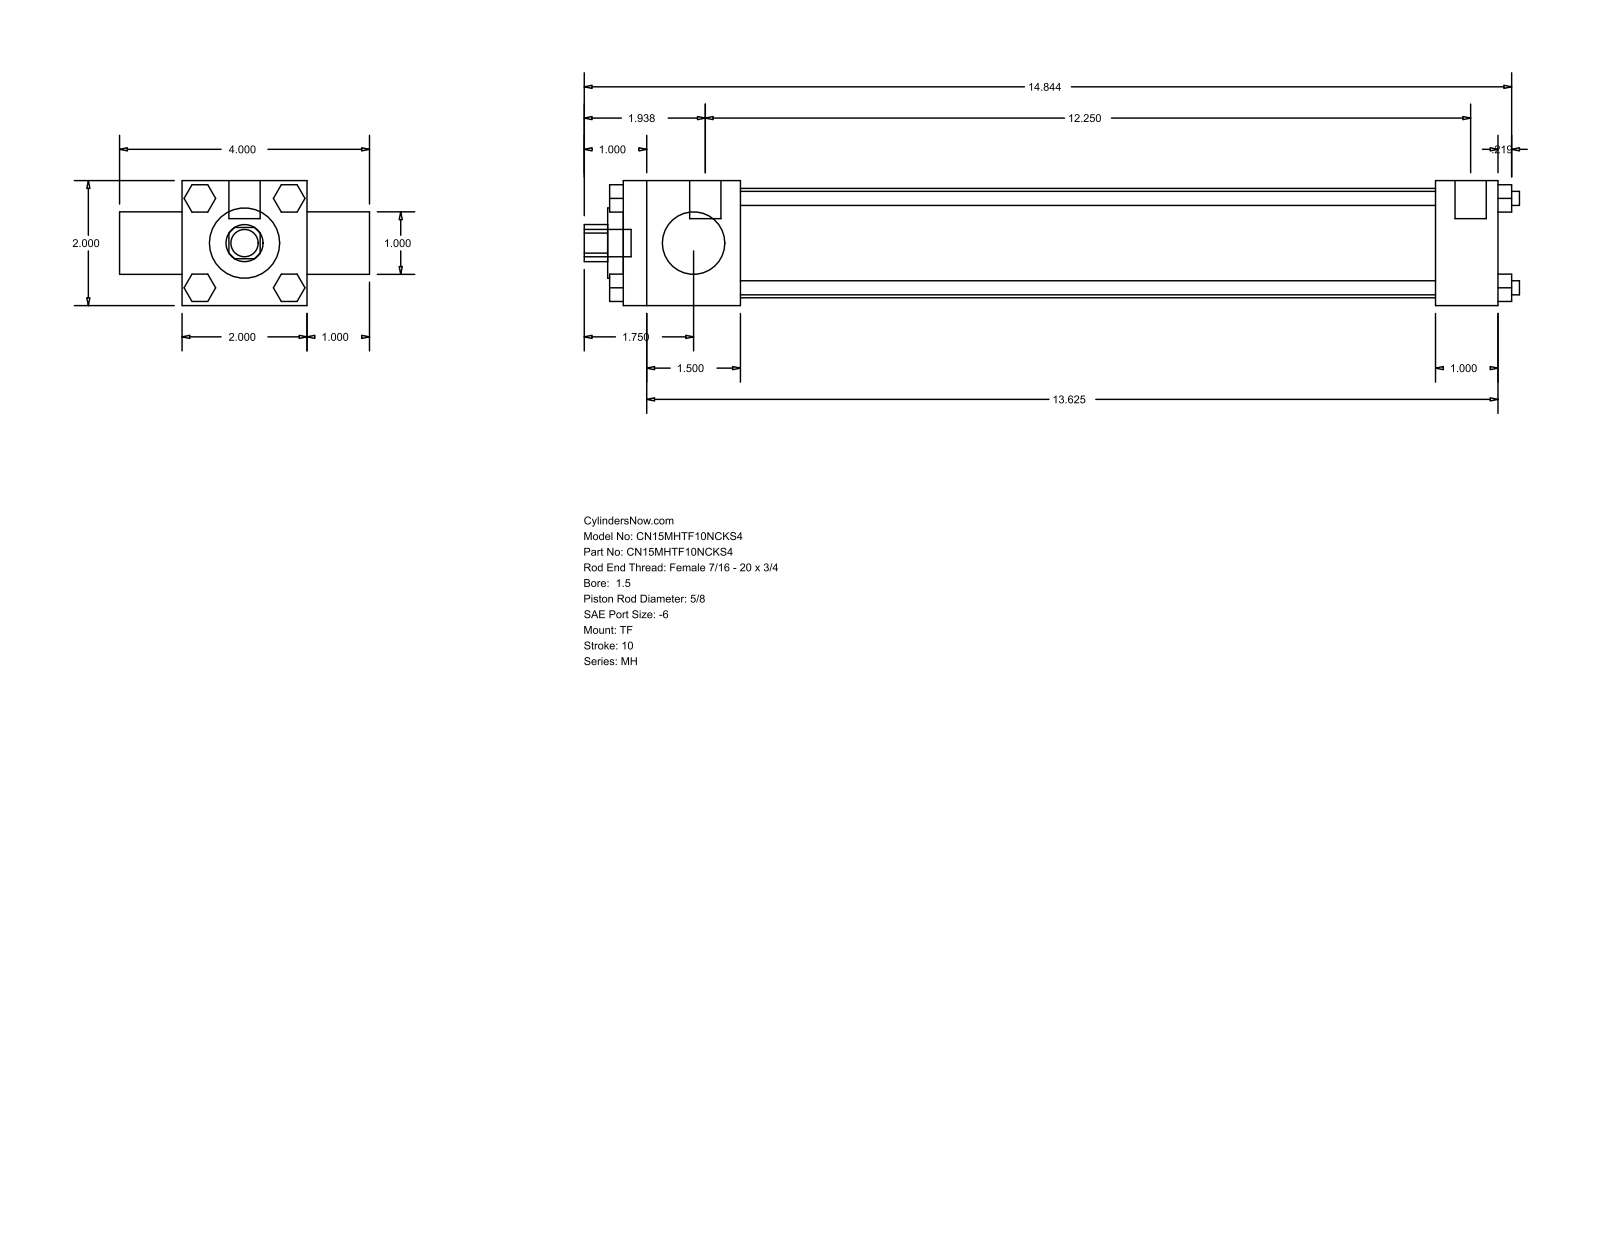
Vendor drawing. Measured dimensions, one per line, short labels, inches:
name: MH_TF__0150_0.625
written by: GSSL Pune (CONFIG_CONTROL_DESIGN)
unit: in
bodies: 0 solids, 120 faces (92 planar, 28 cylindrical, 0 other)
size: 14.969 × 4 × 2
holes: 1× ⌀0.625, 1× ⌀1, 1× ⌀1.125, 1× ⌀1.75
bosses: 4× ⌀0.225, 3× ⌀0.219, 2× ⌀0.5, 1× ⌀0.437
rounds: 1× R0.297
face distances: 2, 14, 1, 3, 1.875, 12.125, 13, 11.125, 1, 0.437
